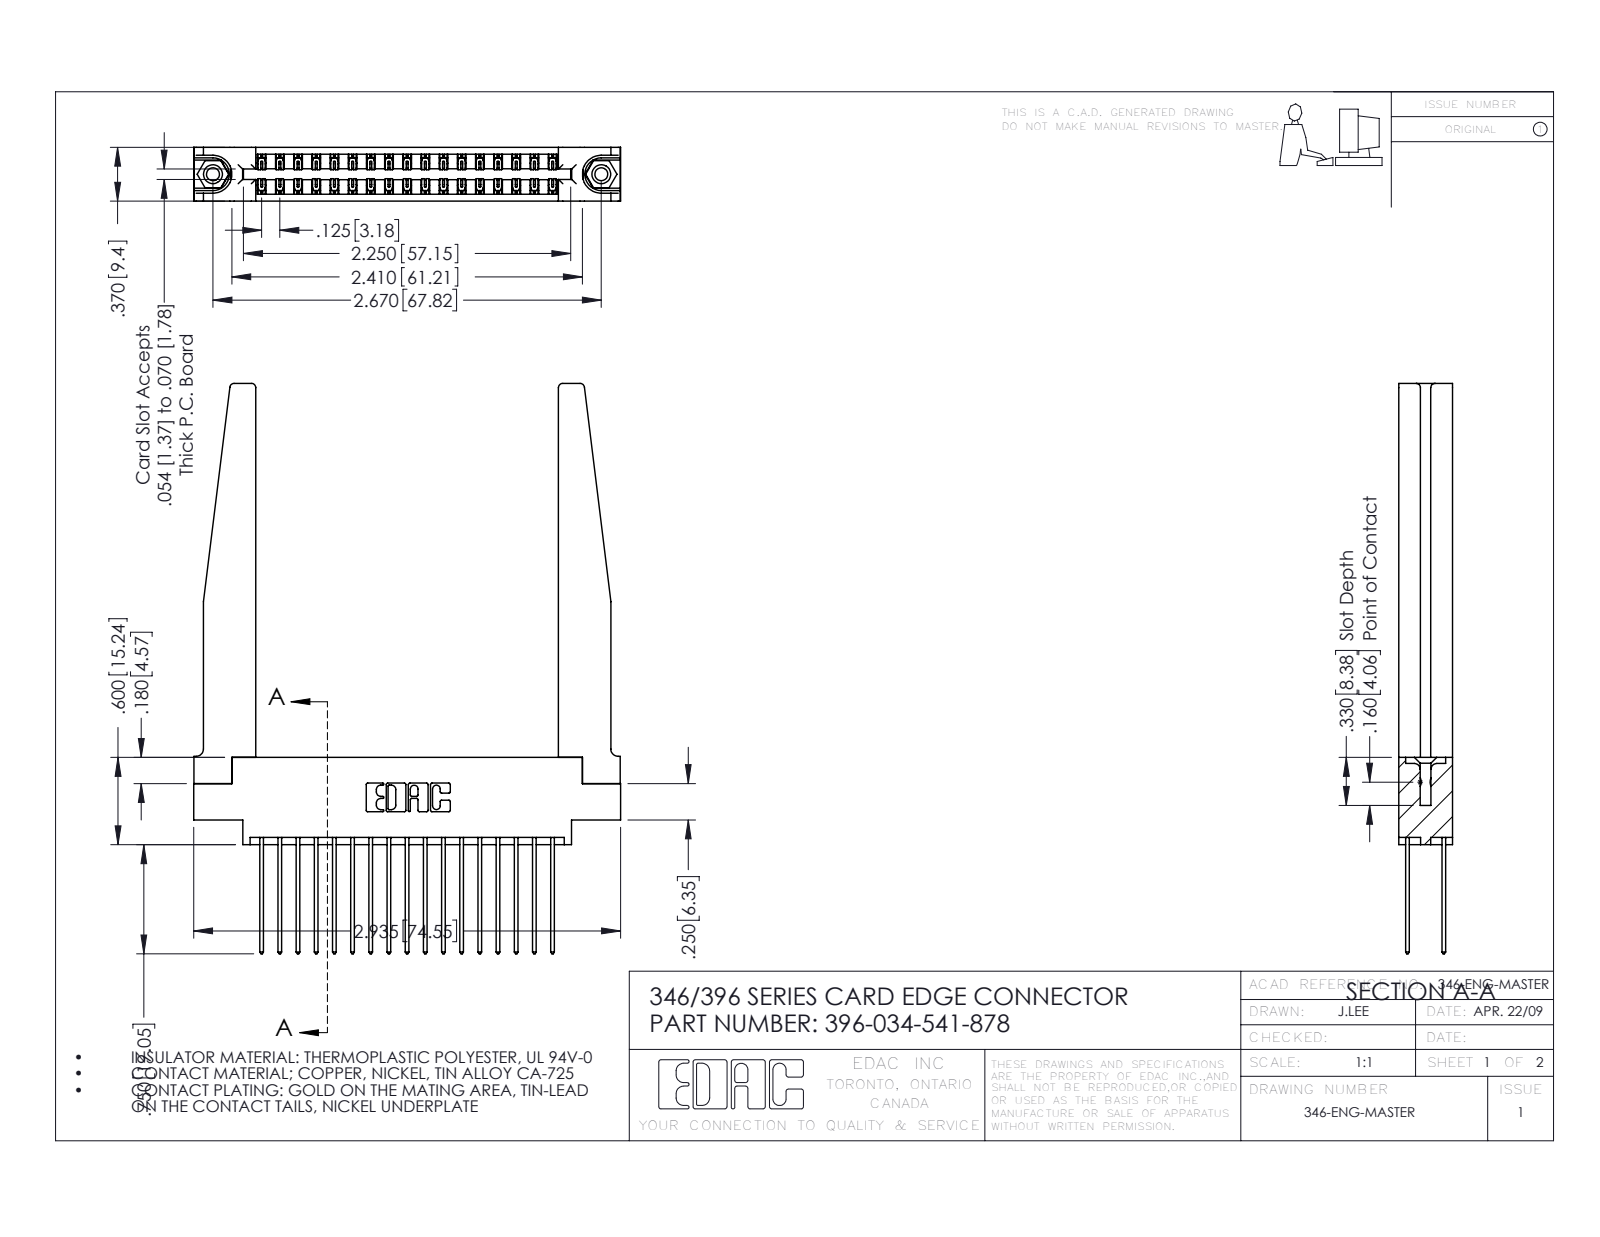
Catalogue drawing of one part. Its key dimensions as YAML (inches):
part_name: "396-034-541-878; 346 Part_0.170 Offset - 0.156 Dia-TH; 346-220-078_345-220-078; 345-250-001_345-250-001-102 (+1 more)"
step_written_by: "SolidWorks 2016 (CONFIG_CONTROL_DESIGN)"
units: inches
bodies: {solids: 39, faces: 2128, planar: 1412, cylindrical: 664, other: 52}
overall_size: [3.92, 2.935, 0.37]
volume: 0.856
surface_area: 26.41
round_holes:
  - {diameter: 0.089, count: 2}
  - {diameter: 0.125, count: 2}
  - {diameter: 0.156, count: 2}
  - {diameter: 0.064, count: 1}
round_bosses_or_shafts:
  - {diameter: 0.155, count: 2}
partial_cylinders:
  - {radius: 0.006, count: 51}
  - {radius: 0.01, count: 34}
  - {radius: 0.01, count: 22}
  - {radius: 0.03, count: 8}
  - {radius: 0.007, count: 6}
  - {radius: 0.031, count: 6}
  - {radius: 0.026, count: 3}
  - {radius: 0.014, count: 2}
face_to_face_distances: [0.37, 0.048, 0.322, 0.072, 0.25, 0.148, 0.15, 0.298, 0.025, 0.275]
hole_center_spacings: [0.246, 2.463, 2.67]
